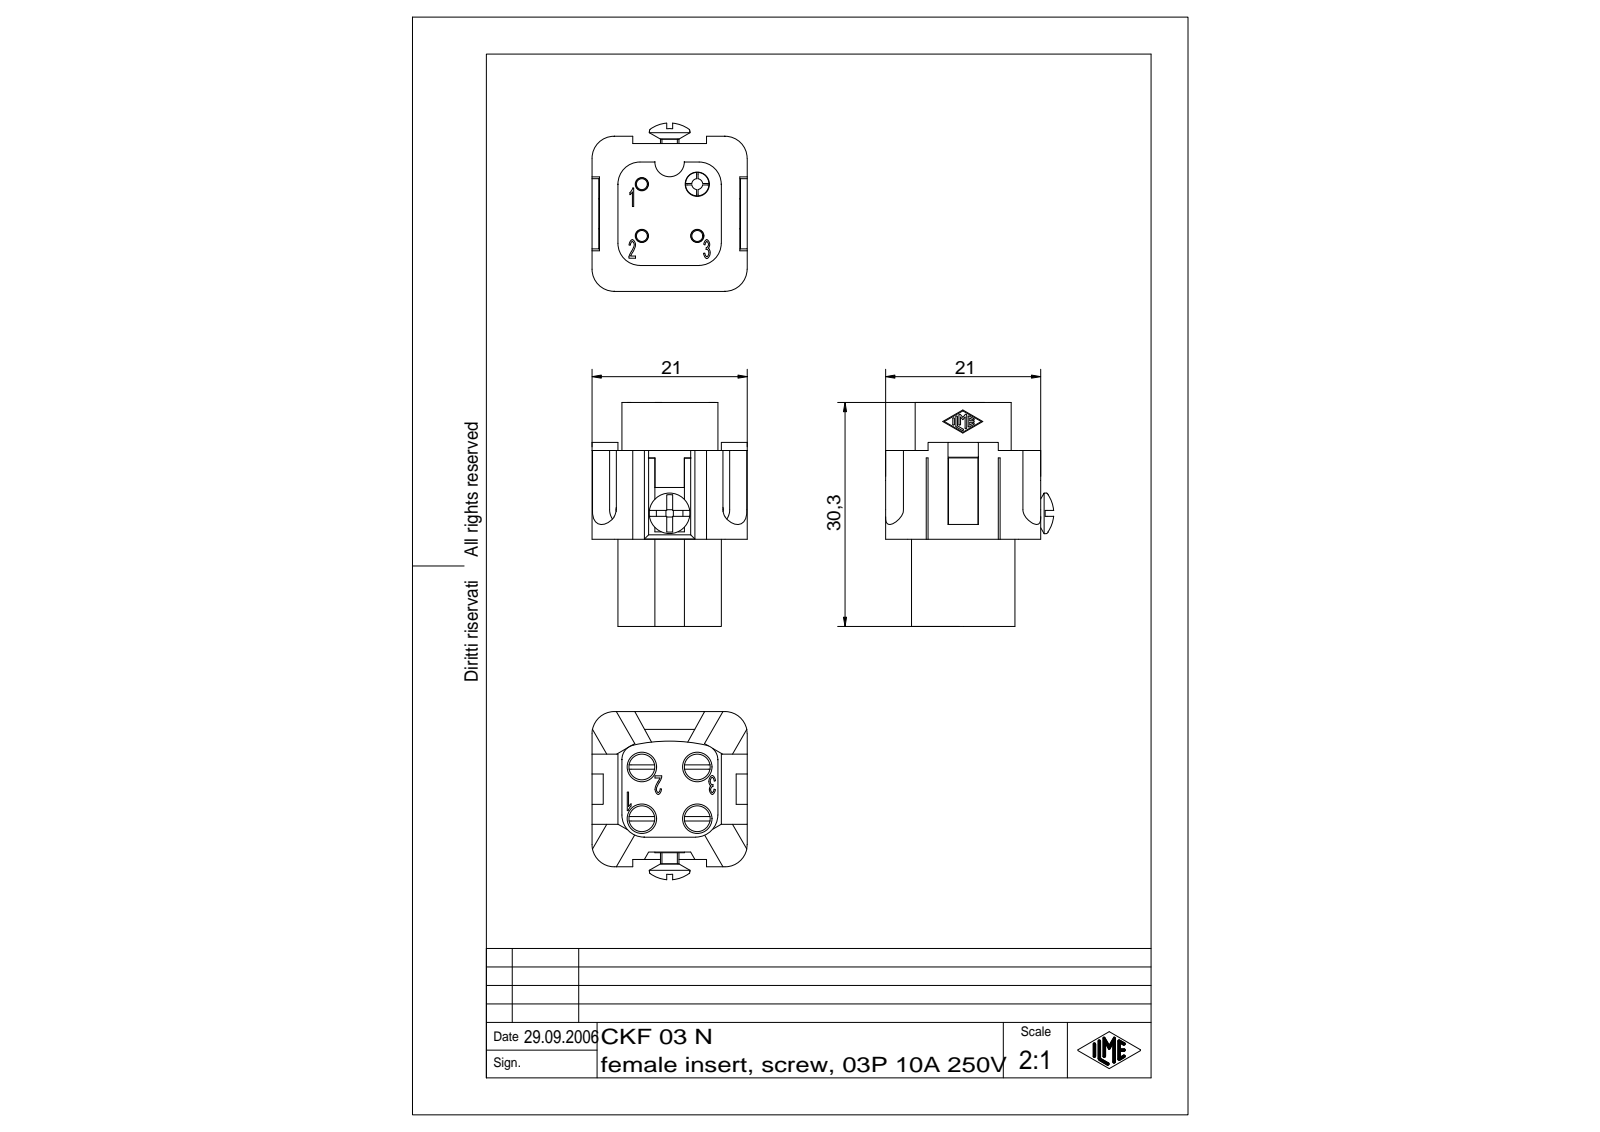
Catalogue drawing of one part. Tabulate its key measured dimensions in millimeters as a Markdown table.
| quantity | value |
| --- | --- |
| part name | CKF 03 N |
| STEP written by | Autodesk Inventor 7 (AUTOMOTIVE_DESIGN) |
| units | millimeters |
| bodies | 8 solids, 445 faces (225 planar, 90 cylindrical, 130 other) |
| overall size | 30.31 × 22.76 × 21 |
| volume | 6 762 mm³ |
| surface area | 4 823 mm² |
| round holes (diameter × count) | 1.5 × 4, 4 × 4, 1.8 × 3, 2 × 2, 3.3 × 1 |
| round bosses / shafts (diameter × count) | 3.5 × 4, 1.7 × 3, 5.5 × 1, 3.2 × 1, 2.5 × 1 |
| partial cylindrical surfaces (radius × count) | 0.1 × 14, 3 × 10, 2 × 5, 0.1 × 4, 22.5 × 1 |
| main face-to-face distances | 3.5, 17.5, 2, 1, 21, 11.8, 14, 15.5, 4, 16.5 |
| hole center spacings | 7, 7.5, 10.26, 6 |
